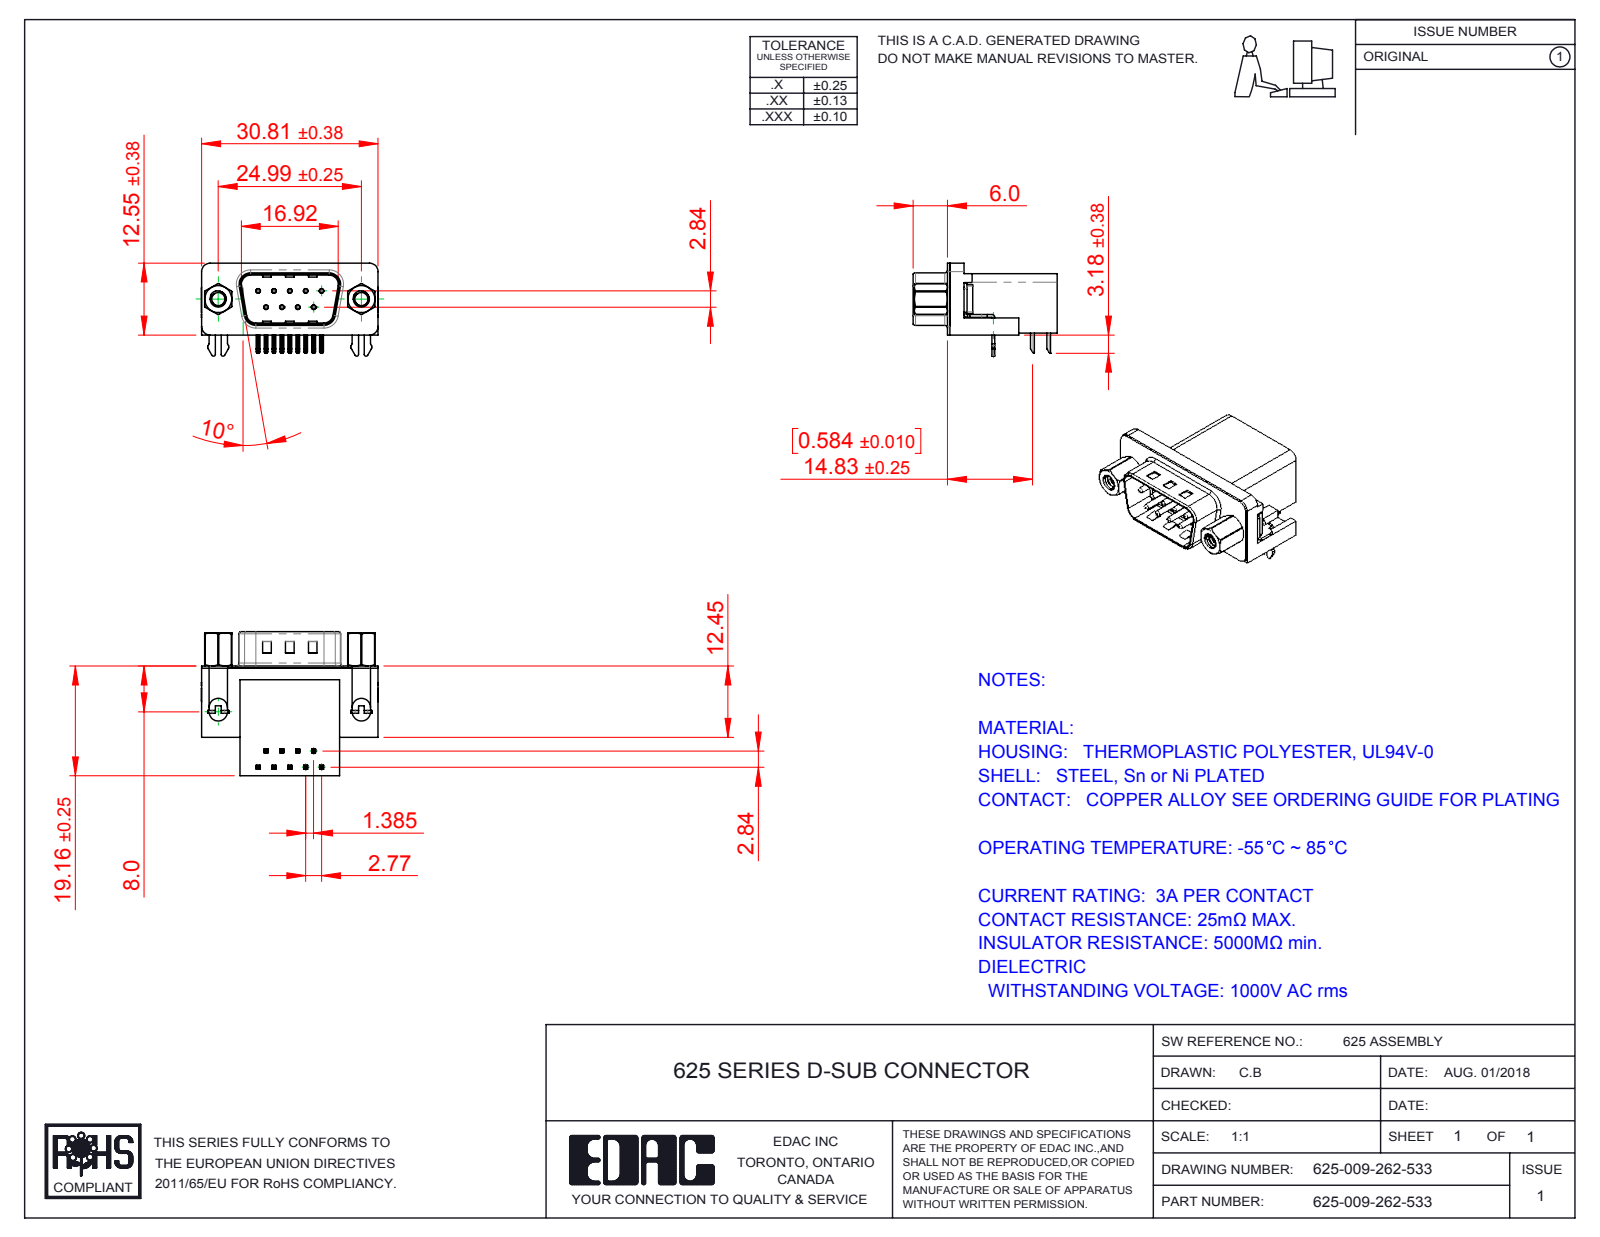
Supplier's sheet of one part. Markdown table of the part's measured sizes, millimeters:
| quantity | value |
| --- | --- |
| part name | 625 4-40 Hex Standoff 5; 625 Contact Bottom; 625 Housing_9 Socket; 625 Shell_9 Socket (+4 more) |
| STEP written by | SolidWorks 2016 (CONFIG_CONTROL_DESIGN) |
| units | millimeters |
| bodies | 17 solids, 1159 faces (627 planar, 397 cylindrical, 135 other) |
| overall size | 30.89 × 25.16 × 16.25 |
| volume | 4 688 mm³ |
| surface area | 5 440 mm² |
| round holes (diameter × count) | 0.35 × 9, 0.8 × 9, 2.26 × 2, 2.29 × 2, 4 × 2, 4.8 × 2, 5 × 2 |
| round bosses / shafts (diameter × count) | 0.75 × 9, 4.9 × 2, 4.75 × 2, 3.9 × 2, 2.79 × 2 |
| partial cylindrical surfaces (radius × count) | 0.25 × 44, 0.12 × 18, 1 × 16, 0.5 × 14, 1.5 × 8, 1.6 × 8, 0.32 × 4, 0.9 × 4 |
| main face-to-face distances | 0.4, 10.34, 18.76, 19.16, 16.26, 2.5, 2.9, 0.35, 10.69, 0.5 |
| hole center spacings | 3.16, 2.77, 5.54, 5.03, 5.04, 8.31, 7.48, 7.49 |
